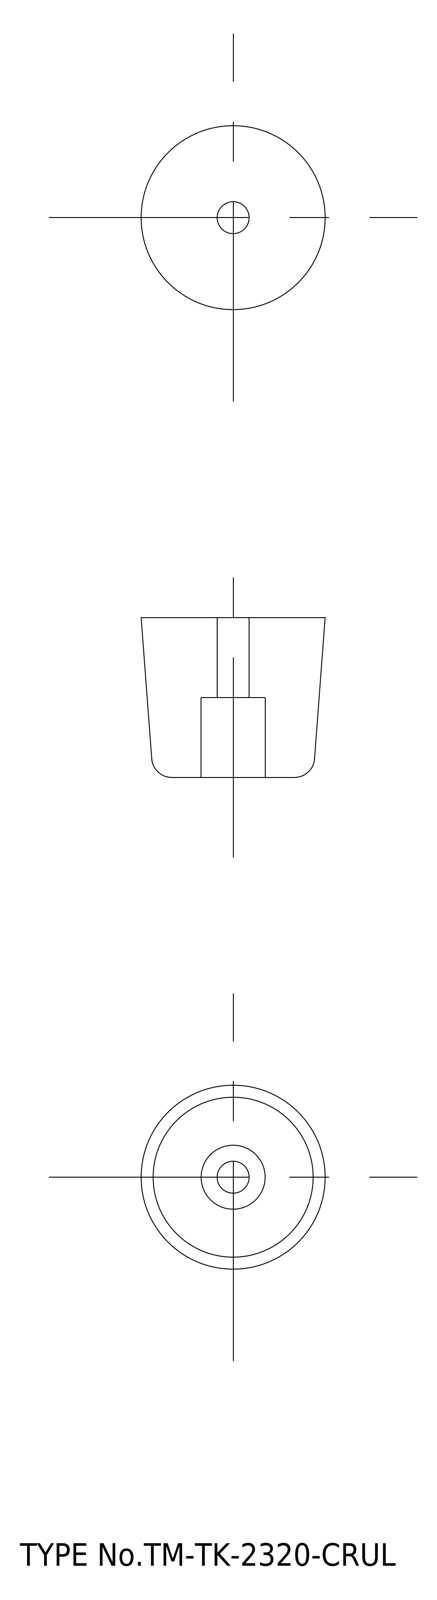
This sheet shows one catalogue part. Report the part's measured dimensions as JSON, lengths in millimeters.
{"part_name": "washer; rubber foot", "step_written_by": "spGate 15.6.1 (AUTOMOTIVE_DESIGN)", "units": "millimeters", "bodies": {"solids": 2, "faces": 20, "planar": 6, "cylindrical": 10, "other": 4}, "overall_size": [23, 23, 20], "volume_mm3": 6591, "surface_area_mm2": 2618, "round_holes": [[4, 1], [8, 1], [10, 1]], "face_to_face_distances": [10, 20, 10.8, 9.2, 0.8]}
